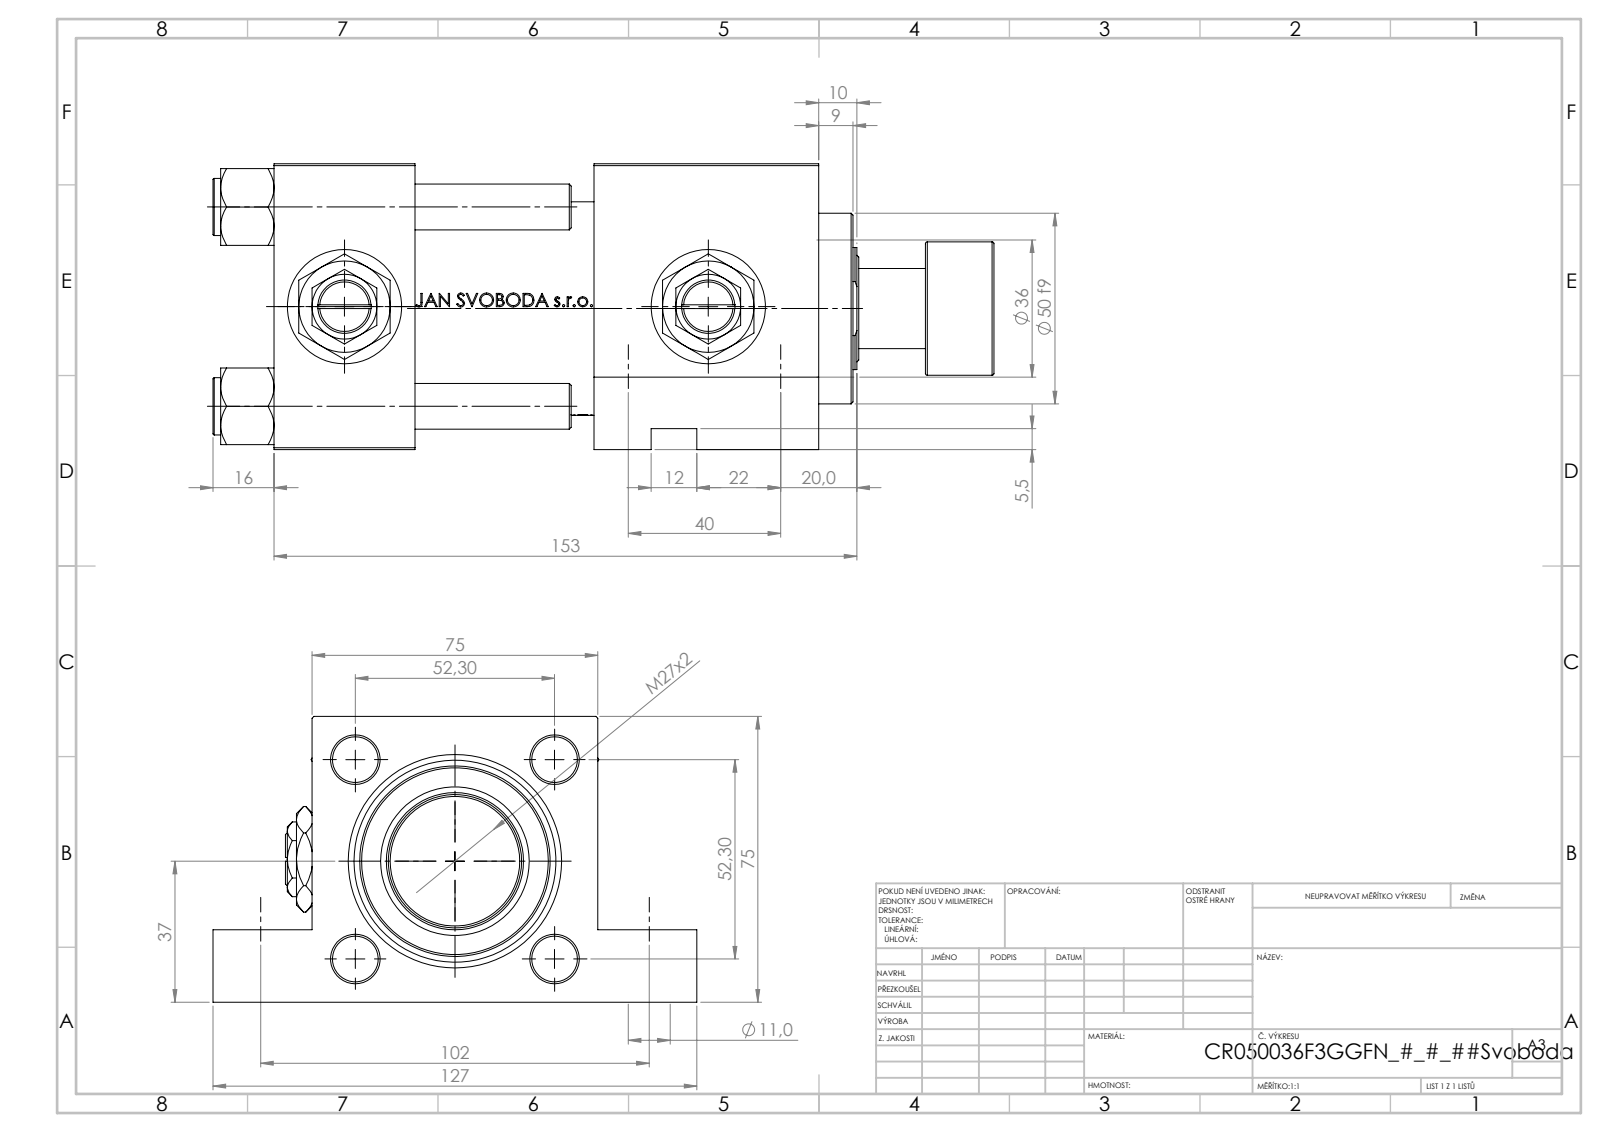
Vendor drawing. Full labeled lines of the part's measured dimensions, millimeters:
Part name (STEP PRODUCT): V215CR_F_TYCINKA; V215CR_F_Body; Zatka_pro_OIL_PORT; V215CR_ROD_END_F (+3 more)
STEP written by: SolidWorks 2019 (CONFIG_CONTROL_DESIGN)
Units: millimetres
Bodies: 14 solids, 1216 faces (488 planar, 140 cylindrical, 588 other)
Overall size (bounding box): 205 × 127 × 75
Volume: 696 712 mm³ · Surface area: 163 229 mm²
Round holes (diameter × count): ⌀12 ×4, ⌀20.96 ×4, ⌀30 ×4, ⌀7 ×3, ⌀11 ×2, ⌀11 ×2, ⌀25.5 ×1, ⌀36 ×1, ⌀39 ×1, ⌀41 ×1, ⌀53 ×1
Round bosses / shafts (diameter × count): ⌀15 ×4, ⌀56 ×1, ⌀50 ×1, ⌀35 ×1, ⌀21 ×1
Main face-to-face distances: 75, 37, 47, 84, 59, 143, 106, 19, 56, 74.8
Hole centre spacings: 52.3, 36.63, 37.34, 40, 51.62, 60.21, 73.96, 90.28
